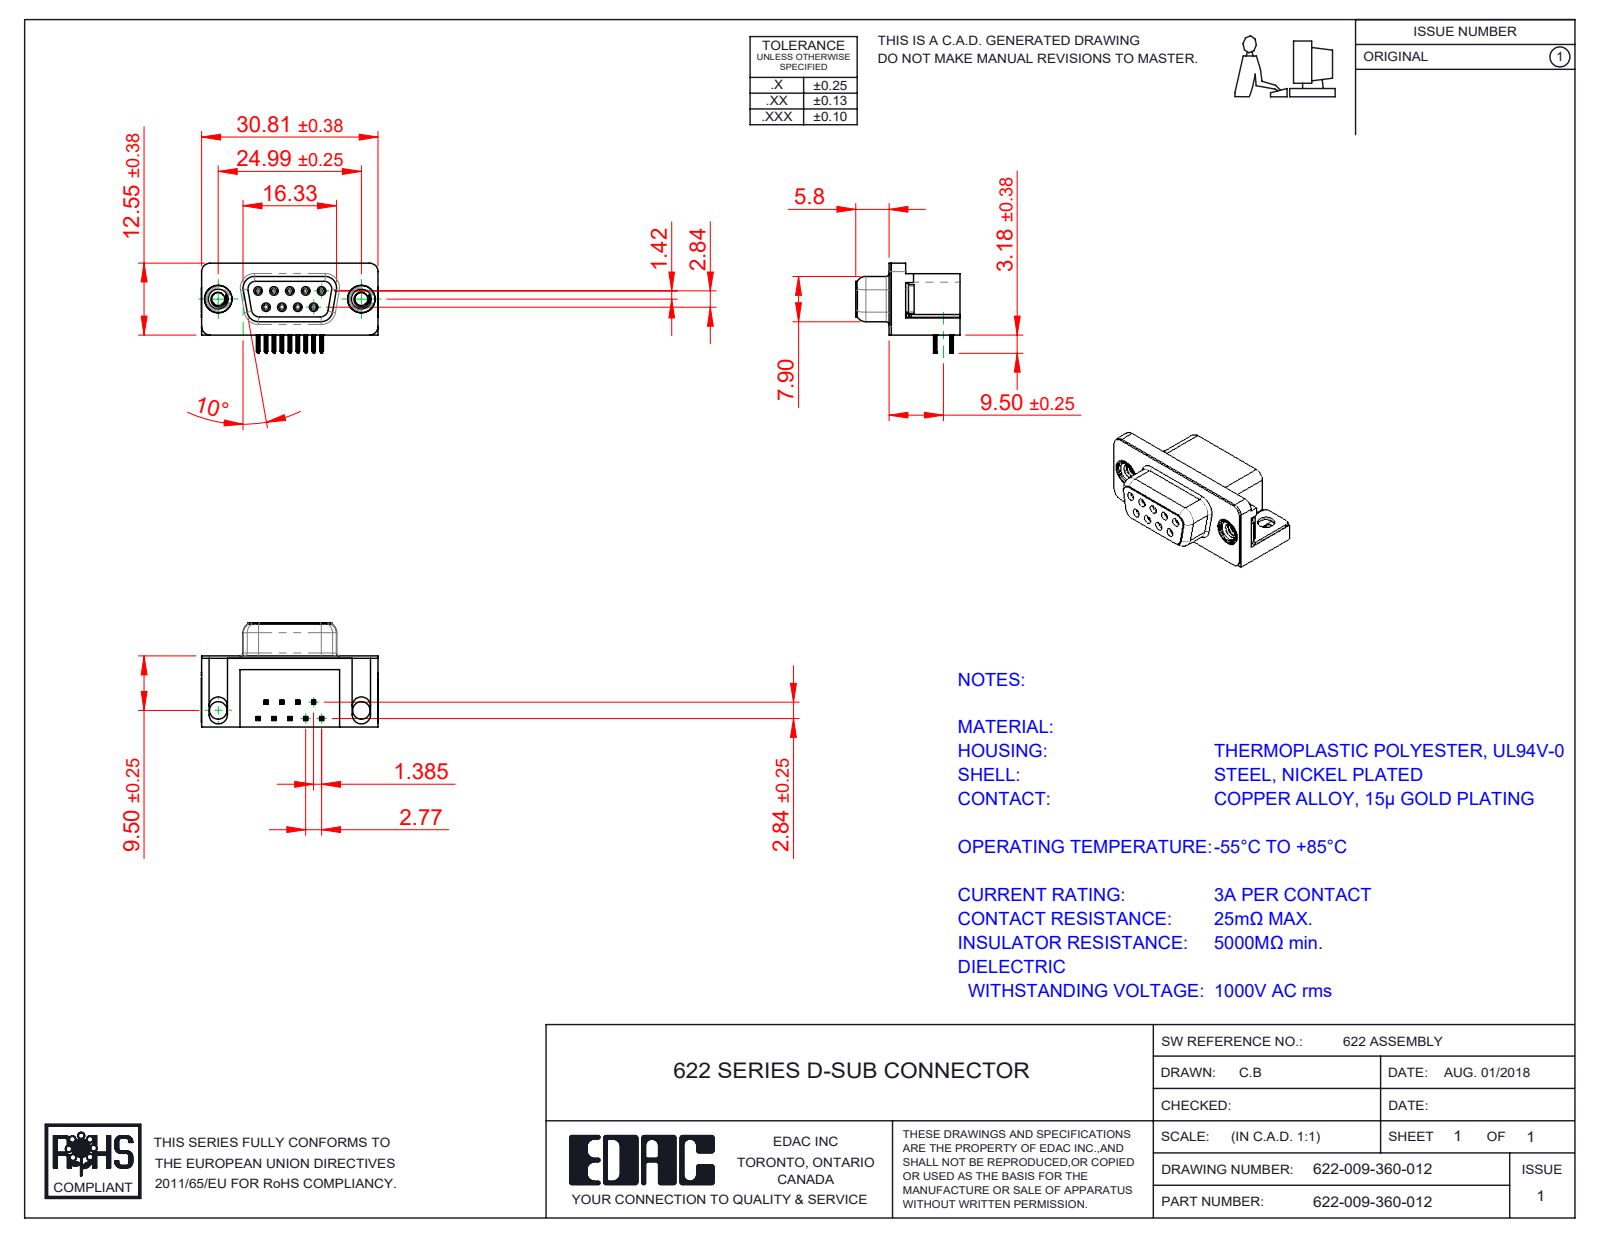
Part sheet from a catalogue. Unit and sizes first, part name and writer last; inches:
Units: inches
Overall size (bounding box): 1.216 × 0.717 × 0.619
Round holes (diameter × count): ⌀0.031 ×9, ⌀0.035 ×9, ⌀0.089 ×2, ⌀0.12 ×2, ⌀0.157 ×2, ⌀0.189 ×2, ⌀0.197 ×2
Round bosses / shafts (diameter × count): ⌀0.047 ×9, ⌀0.193 ×2, ⌀0.187 ×2, ⌀0.154 ×2
Partial cylindrical surfaces — rounded edges, fillets, slot ends (radius × count): R0.004 ×72, R0.006 ×36, R0.014 ×18, R0.039 ×18, R0.013 ×9, R0.01 ×8, R0.053 ×8, R0.063 ×8
Main face-to-face distances: 0.016, 0.472, 0.488, 0.014, 0.114, 0.098, 0.244, 0.407, 0.02, 0.374
Hole centre spacings: 0.124, 0.109, 0.218, 0.198, 0.198, 0.327, 0.294, 0.295
Volume: 0.227 in³ · Surface area: 7.845 in²
Bodies: 15 solids, 1570 faces (682 planar, 416 cylindrical, 472 other)
Part name (STEP PRODUCT): 622 Thru Hole Board Mount; 622-009-360-012; 622 Contact Top; 622 Shell_9 Socket (+3 more)
STEP written by: SolidWorks 2016 (CONFIG_CONTROL_DESIGN)
